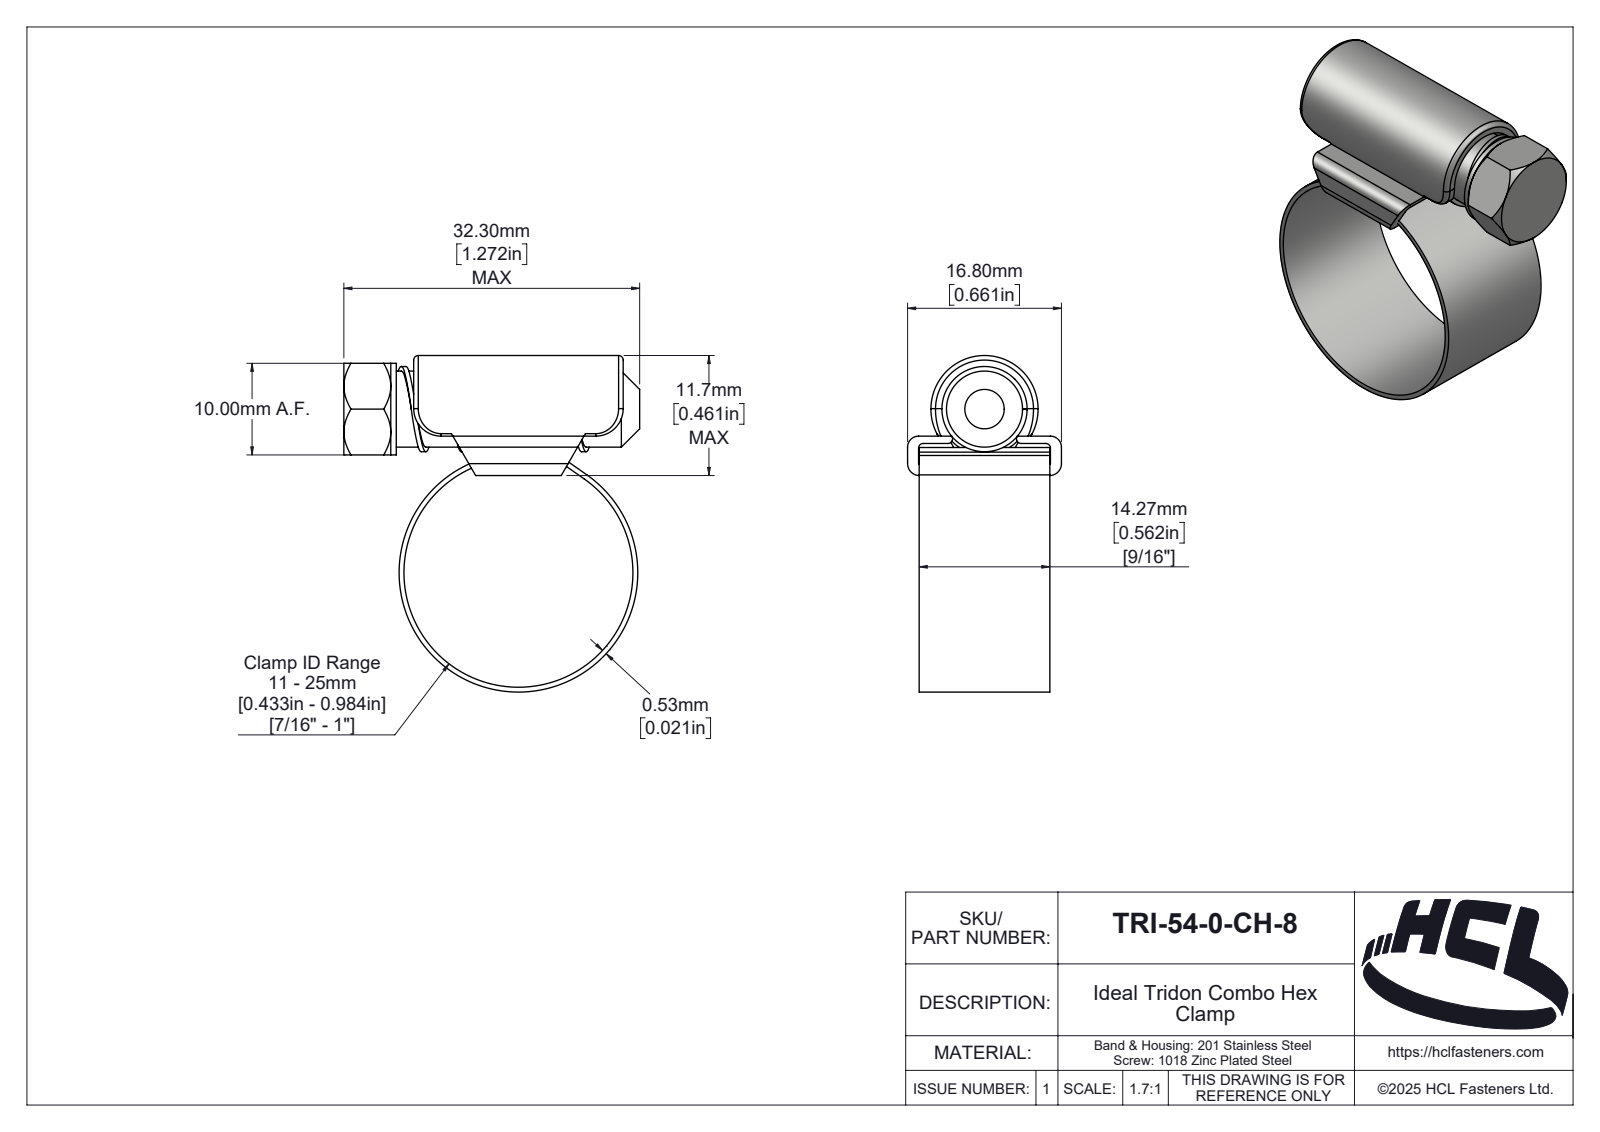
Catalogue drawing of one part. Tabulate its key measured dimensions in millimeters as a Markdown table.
| quantity | value |
| --- | --- |
| part name | TRI-54-0-CH-8 |
| STEP written by | SolidWorks 2025 (AUTOMOTIVE_DESIGN) |
| units | millimeters |
| bodies | 3 solids, 212 faces (35 planar, 101 cylindrical, 76 other) |
| overall size | 36.73 × 32.3 × 16.8 |
| volume | 3 529 mm³ |
| surface area | 5 505 mm² |
| round holes (diameter × count) | 25 × 1 |
| round bosses / shafts (diameter × count) | 26.06 × 1, 10 × 1, 8.3 × 1 |
| partial cylindrical surfaces (radius × count) | 0.5 × 6, 3 × 4, 0.1 × 2, 1.2 × 2, 1.3 × 2, 0.46 × 1, 1.89 × 1, 2 × 1 |
| main face-to-face distances | 1.2, 3.5, 2.3, 4.3, 3.1, 0.8, 9.99, 0.53, 14.26, 1.27 |
